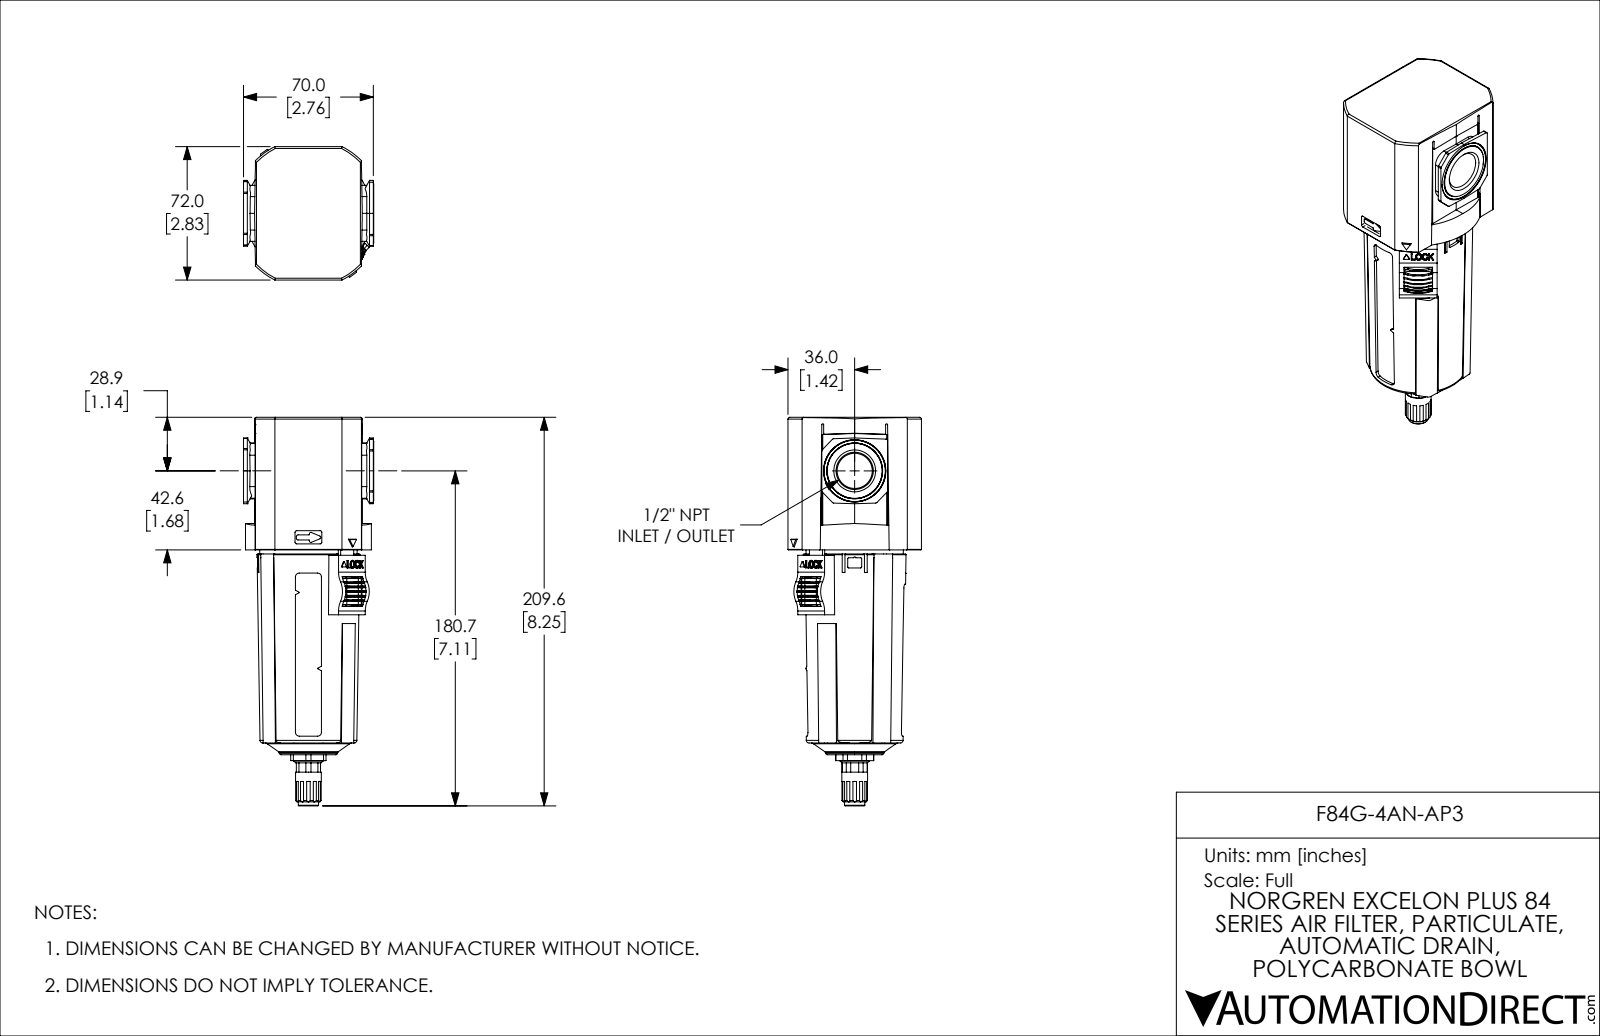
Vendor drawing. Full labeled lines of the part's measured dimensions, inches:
Part name (STEP PRODUCT): F84G-4AN-AP3
STEP written by: SolidWorks 2021 (CONFIG_CONTROL_DESIGN)
Units: inches
Bodies: 5 solids, 1089 faces (504 planar, 405 cylindrical, 180 other)
Overall size (bounding box): 8.251 × 2.835 × 2.766
Volume: 27.87 in³ · Surface area: 149.9 in²
Round holes (diameter × count): ⌀0.163 ×2, ⌀0.22 ×1, ⌀0.246 ×1, ⌀0.776 ×1, ⌀0.969 ×1, ⌀2.461 ×1
Round bosses / shafts (diameter × count): ⌀0.315 ×2, ⌀0.276 ×2, ⌀1 ×1, ⌀0.969 ×1, ⌀0.907 ×1, ⌀0.617 ×1, ⌀0.547 ×1, ⌀0.433 ×1
Partial cylindrical surfaces — rounded edges, fillets, slot ends (radius × count): R0.039 ×44, R0.02 ×40, R0.01 ×24, R0.028 ×16, R0.008 ×10, R0.038 ×8, R0.045 ×8, R0.06 ×8
Main face-to-face distances: 0.059, 2.411, 2.352, 2.835, 0.035, 2.317, 2.376, 2.756, 0.404, 0.439
Hole centre spacings: 0.594, 1.189
